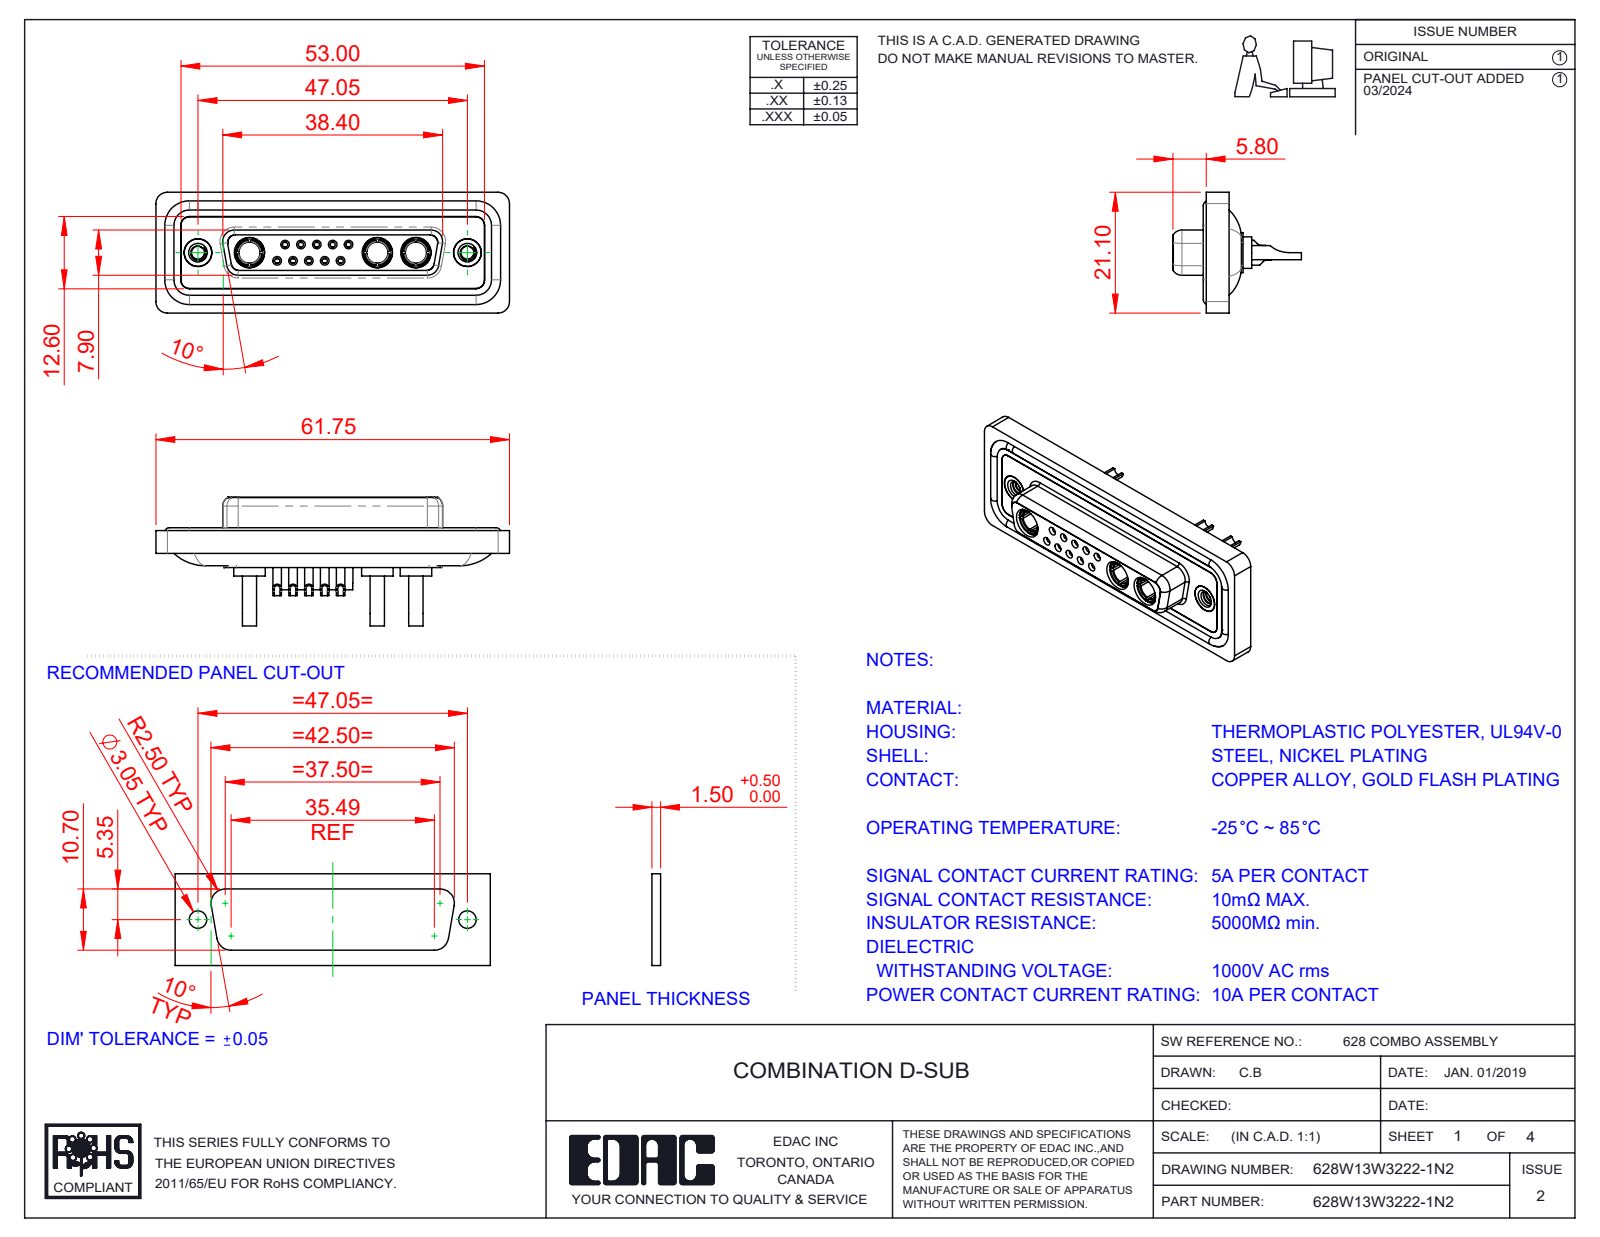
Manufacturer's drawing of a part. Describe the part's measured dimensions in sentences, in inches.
The part is named "628Combo Housing_13W3; 628Combo Waterproof Housing_25 Contacts; 628W13W3222-1N2; 628Combo Threaded Rivet_2 (+5 more)". Its 3-D file was written by "SolidWorks 2023 (CONFIG_CONTROL_DESIGN)". It is 23 solids with 1173 faces: 368 planar, 476 cylindrical and 329 other. Overall it measures 2.431 by 0.884 by 0.831 inches. Its volume is 0.506 cubic inches and its surface area 21.63 square inches. Round holes: 10 of diameter 0.035, 10 of diameter 0.039, 10 of diameter 0.043, 10 of diameter 0.059, 10 of diameter 0.079, 5 of diameter 0.063, 5 of diameter 0.067, 5 of diameter 0.191, 3 of diameter 0.067, 3 of diameter 0.146, 3 of diameter 0.209, 2 of diameter 0.089. Round bosses or shafts: 10 of diameter 0.087, 9 of diameter 0.063, 3 of diameter 0.217, 3 of diameter 0.205, 3 of diameter 0.195, 3 of diameter 0.187, 3 of diameter 0.148, 3 of diameter 0.098. Partial cylindrical surfaces (rounded edges, fillets, slot ends): 22 of radius 0.059, 18 of radius 0.079, 8 of radius 0.053, 8 of radius 0.063, 6 of radius 0.039, 4 of radius 0.01, 4 of radius 0.02, 4 of radius 0.024. The main face-to-face distances are 0.016, 0.071, 0.293, 0.222, 0.02, 0.26, 0.278, 0.063, 0.114, 0.043. The hole center spacings are 0.124, 0.109, 0.198, 0.198, 0.218, 0.327, 0.295, 0.109.
